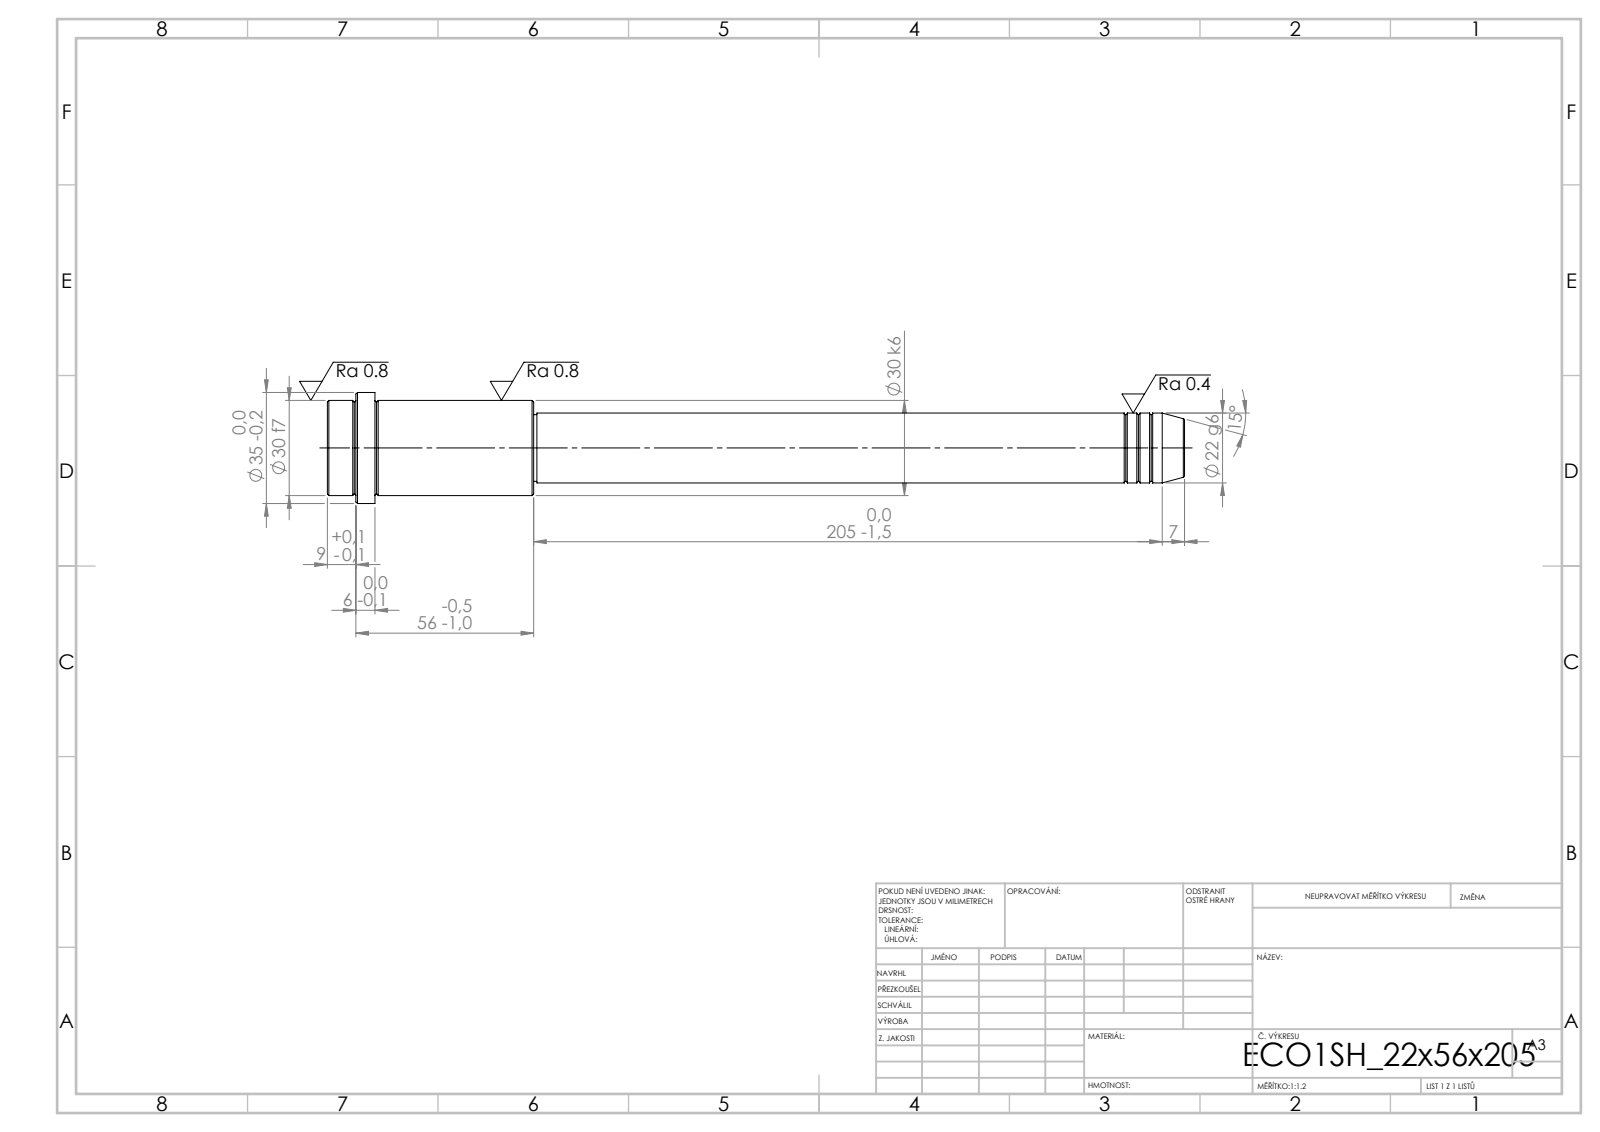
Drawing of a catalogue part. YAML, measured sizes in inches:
step_written_by: "SolidWorks 2019 (CONFIG_CONTROL_DESIGN)"
units: inches
bodies: {solids: 1, faces: 52, planar: 6, cylindrical: 16, other: 30}
overall_size: [10.63, 1.378, 1.378]
volume: 7.613
surface_area: 34.64
round_bosses_or_shafts:
  - {diameter: 1.378, count: 1}
  - {diameter: 1.181, count: 1}
  - {diameter: 0.866, count: 1}
  - {diameter: 0.827, count: 1}
face_to_face_distances: [2.559, 1.969, 0.591, 8.071, 10.039, 10.63, 10.276, 2.205, 0.236, 0.354]
